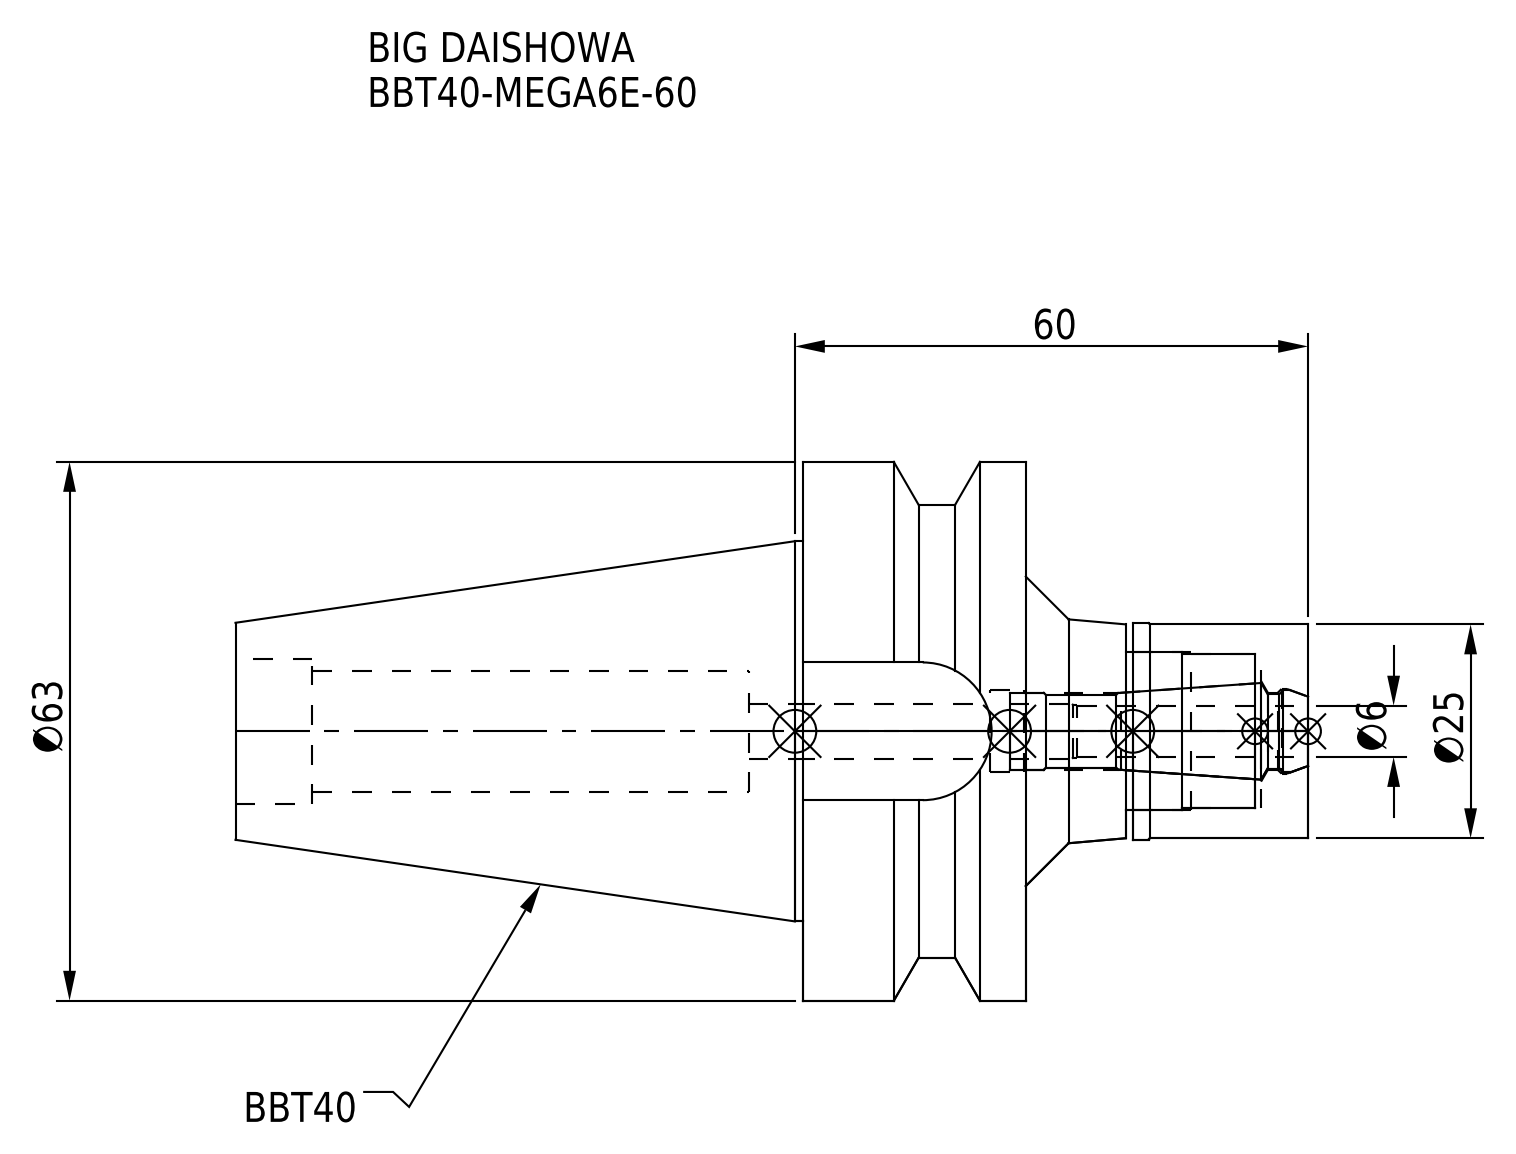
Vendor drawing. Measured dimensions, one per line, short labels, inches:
name: BBT40ME06060-060_ASM.stp; BBT40-MEGA6E-60-060-FreeParts; BBT40-MEGA6E-60-060.stp; BBT40-MEGA6E-60_1.stp (+3 more)
written by: SolidWorks 2019 (CONFIG_CONTROL_DESIGN)
unit: in
bodies: 2 solids, 78 faces (20 planar, 38 cylindrical, 20 other)
size: 4.937 × 2.48 × 2.48
volume: 8.501 in³; area: 43.49 in²
holes: 1× ⌀0.252, 1× ⌀0.354, 1× ⌀0.378, 1× ⌀0.39, 1× ⌀0.559, 1× ⌀0.669, 1× ⌀0.709, 1× ⌀0.728
bosses: 1× ⌀2.48, 1× ⌀2.087, 1× ⌀1.75, 1× ⌀0.996, 1× ⌀0.984
rounds: 1× R0.317
face distances: 1.024, 1.299, 2.323, 1.772, 4.937, 3.638, 2.614, 0.807, 0.492, 1.516
